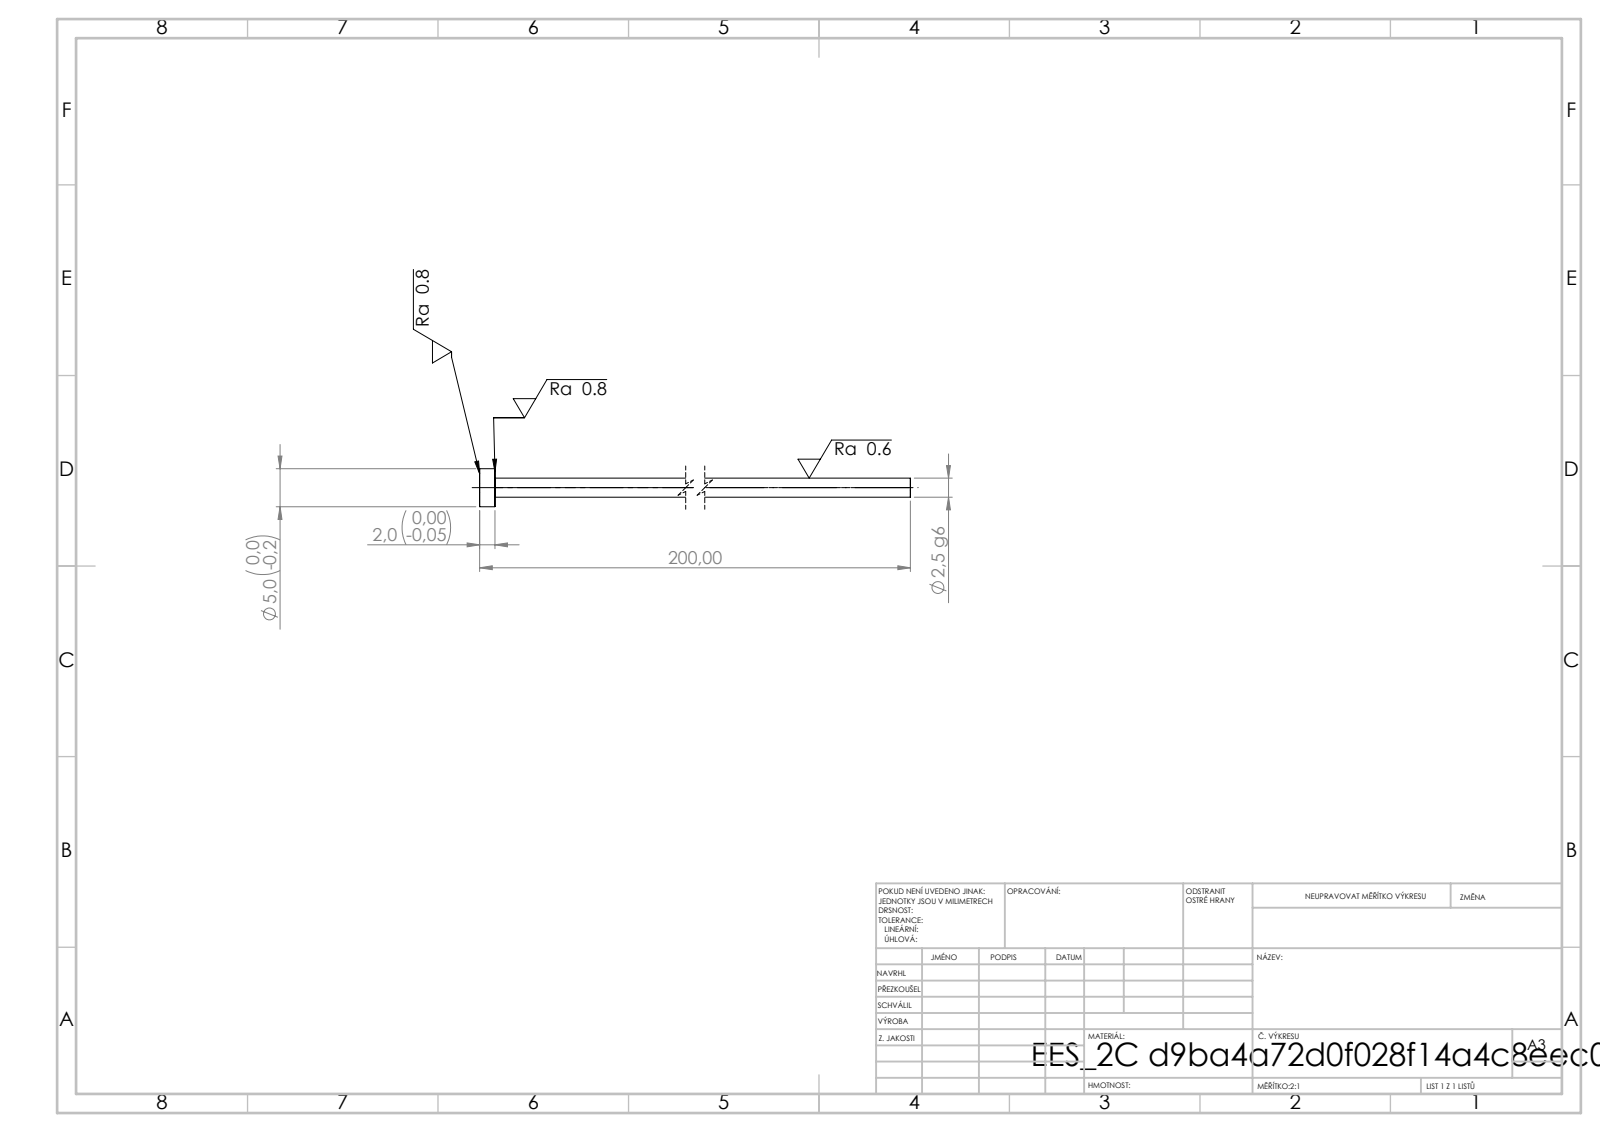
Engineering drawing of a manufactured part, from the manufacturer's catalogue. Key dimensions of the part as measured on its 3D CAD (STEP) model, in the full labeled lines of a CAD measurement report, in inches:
STEP written by: SolidWorks 2019 (CONFIG_CONTROL_DESIGN)
Units: inches
Bodies: 1 solid, 7 faces (3 planar, 4 cylindrical, 0 other)
Overall size (bounding box): 7.874 × 0.197 × 0.197
Volume: 0.062 in³ · Surface area: 2.52 in²
Round bosses / shafts (diameter × count): ⌀0.197 ×1, ⌀0.098 ×1
Main face-to-face distances: 0.079, 7.874, 7.795
